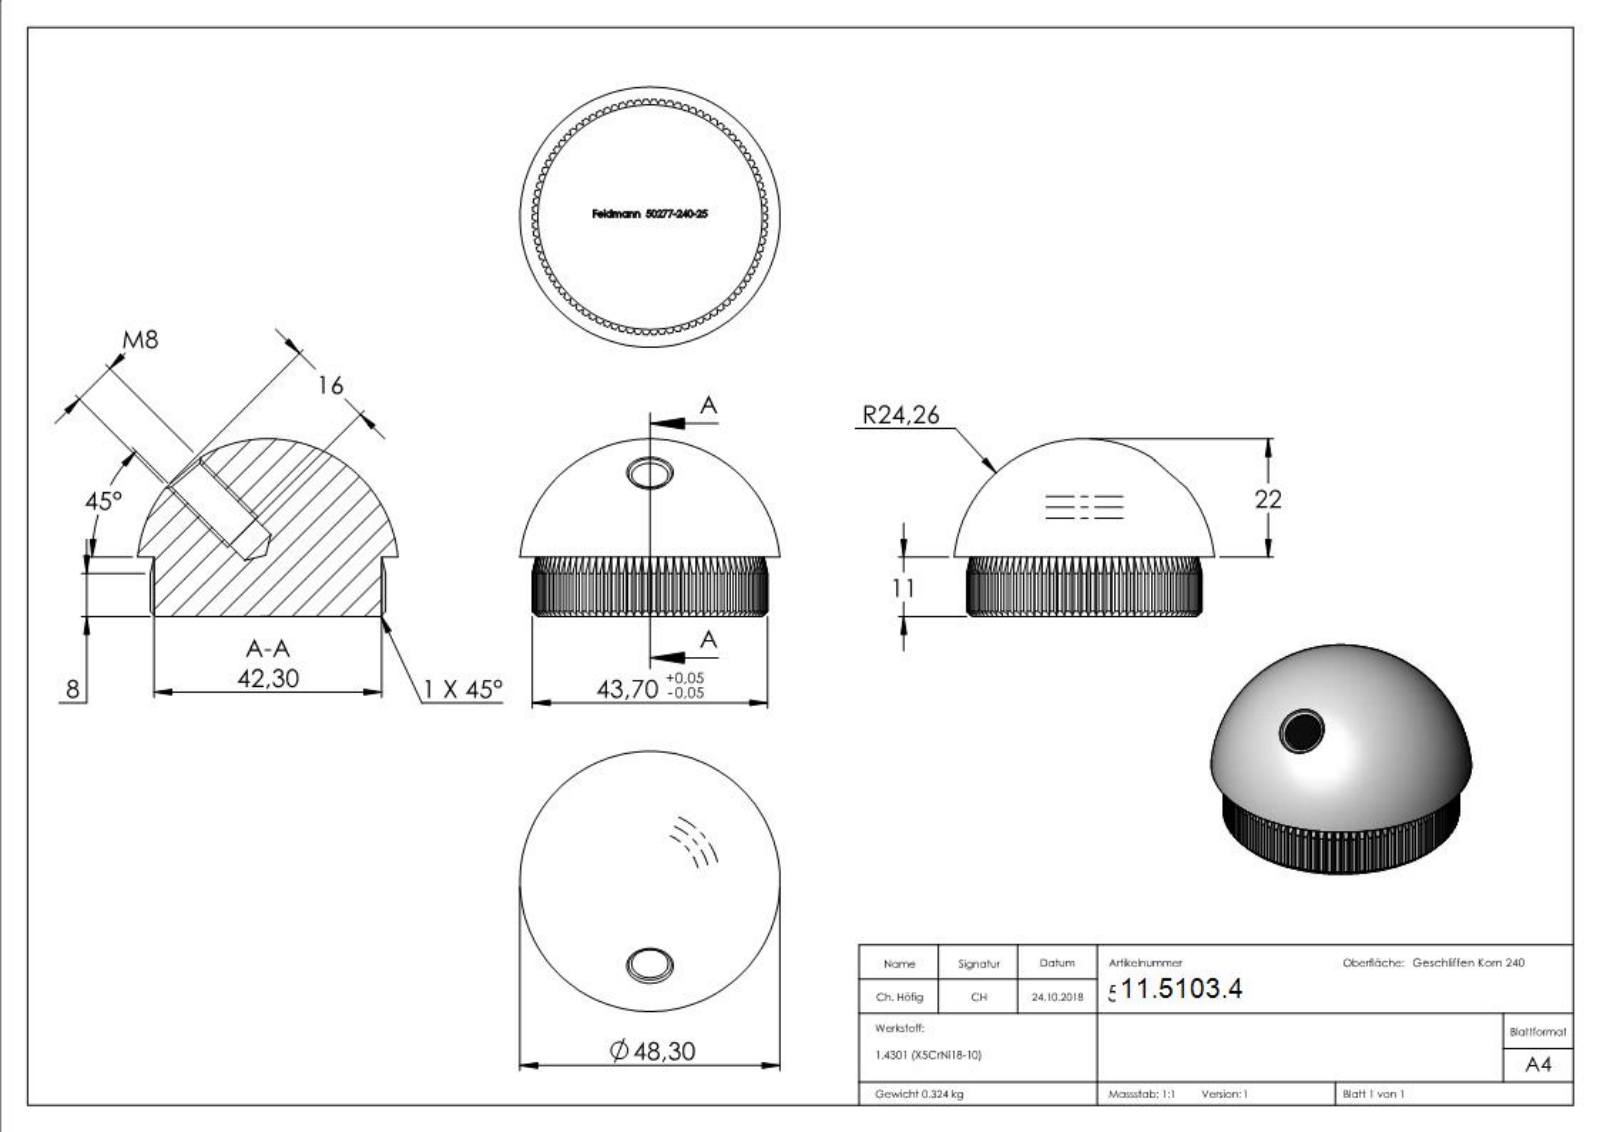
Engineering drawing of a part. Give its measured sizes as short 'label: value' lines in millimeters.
name: 50277-240-25
written by: SolidWorks 2015 (CONFIG_CONTROL_DESIGN)
unit: mm
bodies: 1 solid, 590 faces (306 planar, 92 cylindrical, 192 other)
size: 48.3 × 48.3 × 33
volume: 41 053 mm³; area: 7 765 mm²
holes: 1× ⌀6.8
rounds: 1× R21.85
face distances: 11, 21.15, 21.14, 21.16, 21.18, 21.12, 10.9, 10.58, 10.57, 1.32
